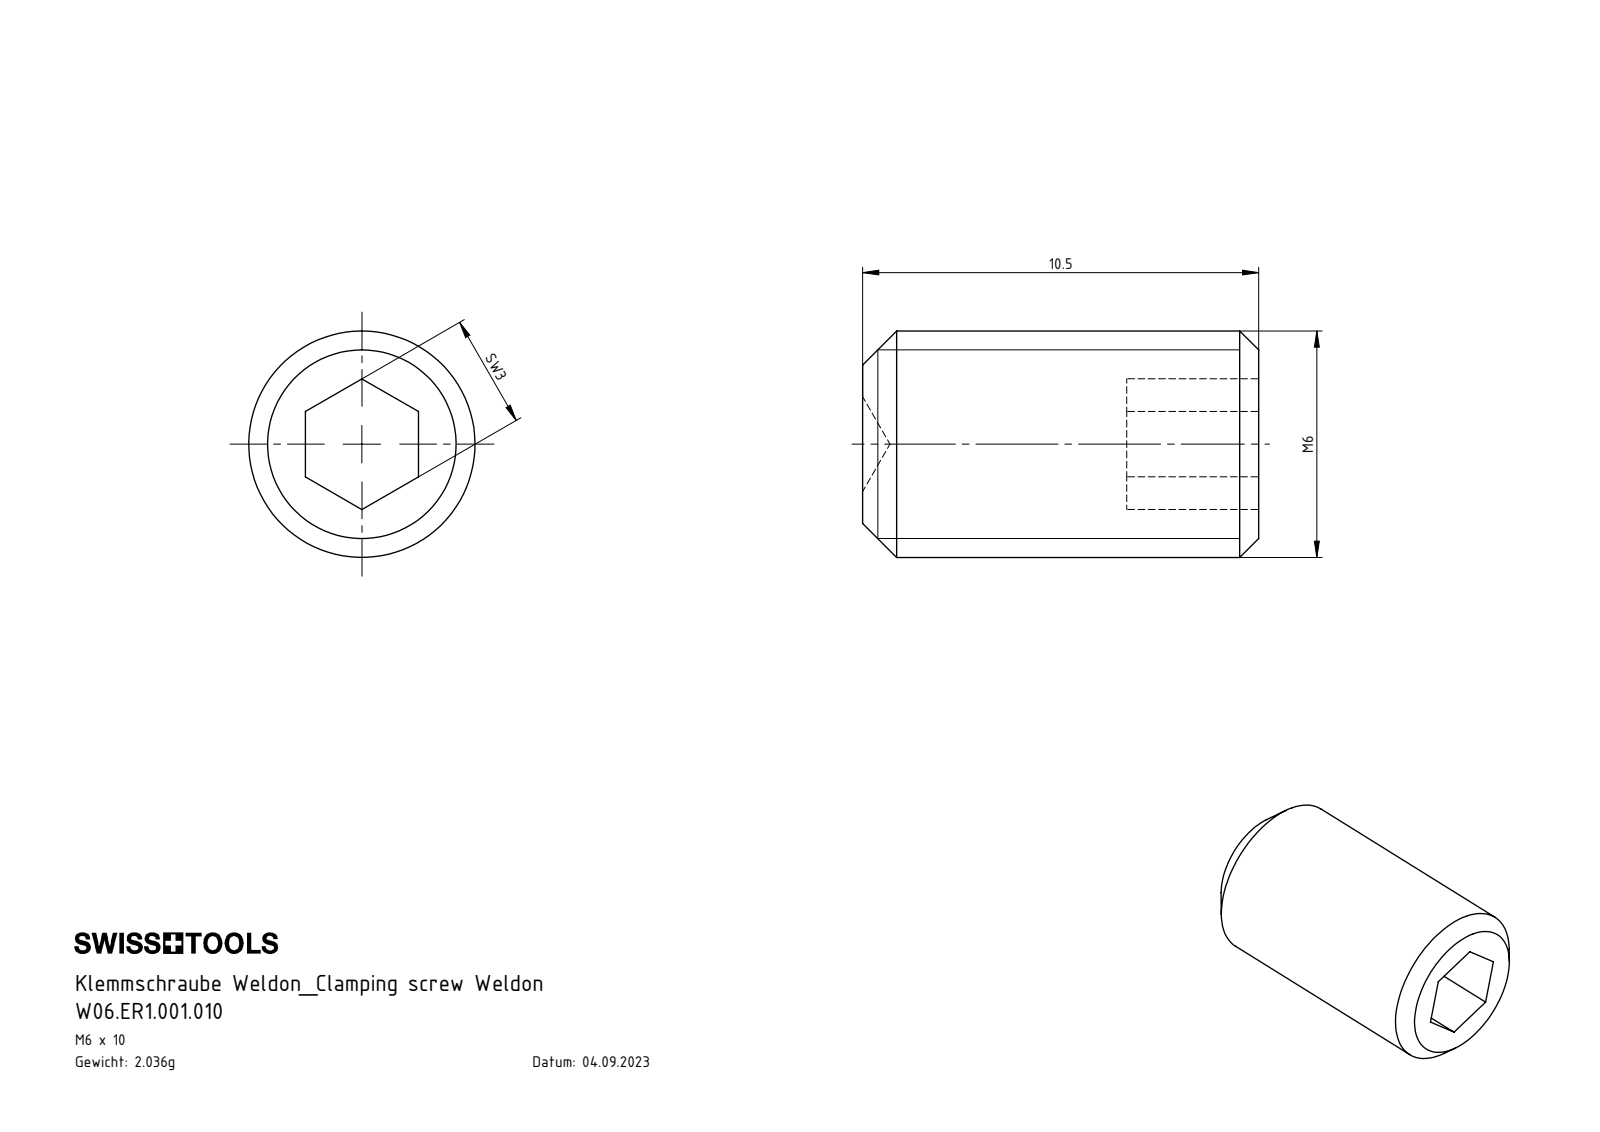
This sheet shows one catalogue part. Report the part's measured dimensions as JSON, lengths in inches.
{"part_name": "W06.ER1.001.010", "step_written_by": "SolidWorks 2017 (AUTOMOTIVE_DESIGN)", "units": "inches", "bodies": {"solids": 1, "faces": 17, "planar": 9, "cylindrical": 2, "other": 6}, "overall_size": [0.413, 0.236, 0.236], "volume_in3": 0.016, "surface_area_in2": 0.426, "round_bosses_or_shafts": [[0.236, 1]], "face_to_face_distances": [0.118, 0.413, 0.138, 0.276]}
